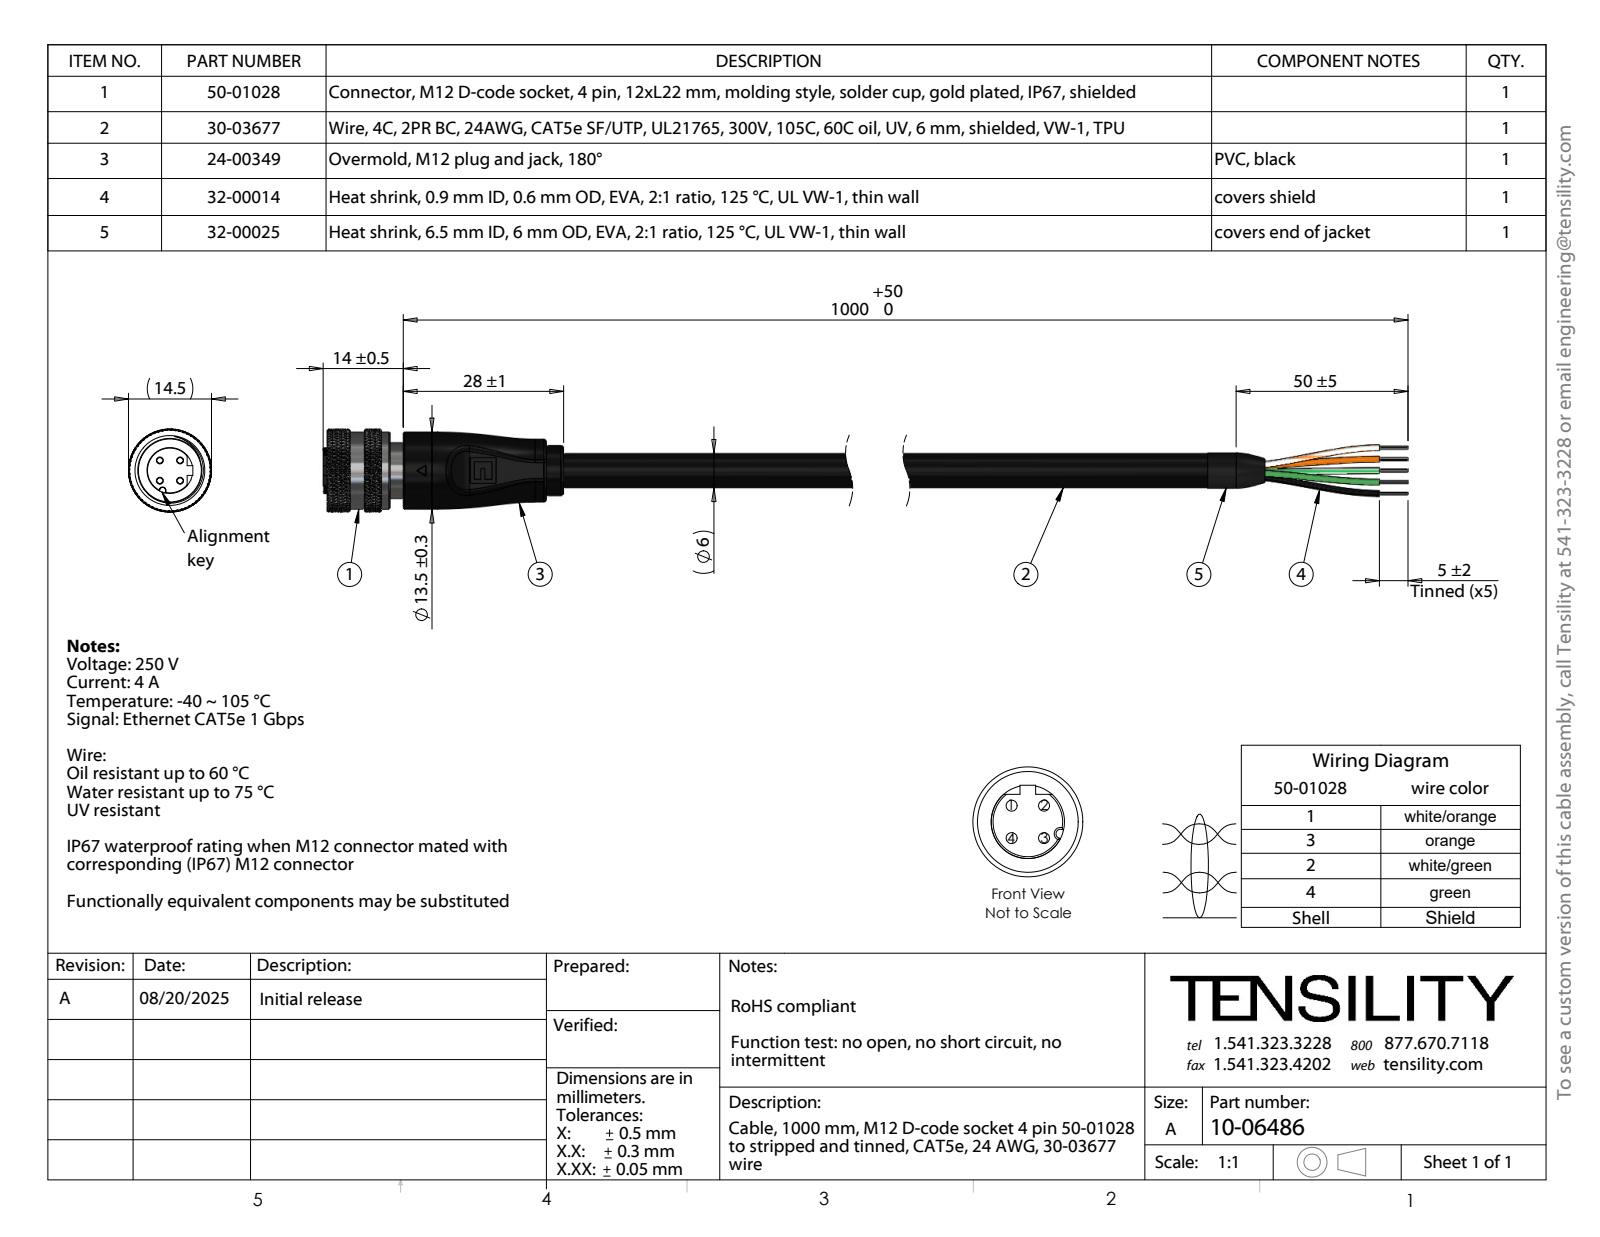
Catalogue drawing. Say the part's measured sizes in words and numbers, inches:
The part is named "50-01028-04_默认; 50-01028-05_默认; 50-01028-03_默认; 24-00349_Mexico (+5 more)". Its 3-D file was written by "SolidWorks 2025 (CONFIG_CONTROL_DESIGN)". It is 87 solids with 3550 faces: 339 planar, 940 cylindrical and 2271 other. Overall it measures 8.74 by 0.571 by 0.571 inches. Its volume is 0.587 cubic inches and its surface area 41.89 square inches. Round holes: 28 of diameter 0.008, 4 of diameter 0.041, 4 of diameter 0.043, 4 of diameter 0.047, 1 of diameter 0.124, 1 of diameter 0.126, 1 of diameter 0.132, 1 of diameter 0.354, 1 of diameter 0.394, 1 of diameter 0.441. Round bosses or shafts: 35 of diameter 0.008, 4 of diameter 0.063, 4 of diameter 0.059, 1 of diameter 0.531, 1 of diameter 0.433, 1 of diameter 0.417, 1 of diameter 0.413, 1 of diameter 0.386. Partial cylindrical surfaces (rounded edges, fillets, slot ends): 10 of radius 0.004, 6 of radius 0.016, 2 of radius 0.02, 2 of radius 0.059, 1 of radius 0.157, 1 of radius 0.197, 1 of radius 0.22, 1 of radius 0.266. The main face-to-face distances are 7.008, 1.102, 5.906, 0.276, 0.185, 0.039, 1.252, 0.138, 0.917, 6.823. The hole center spacings are 0.075, 0.014, 0.082, 0.042, 0.035, 0.043, 0.049, 0.071.
